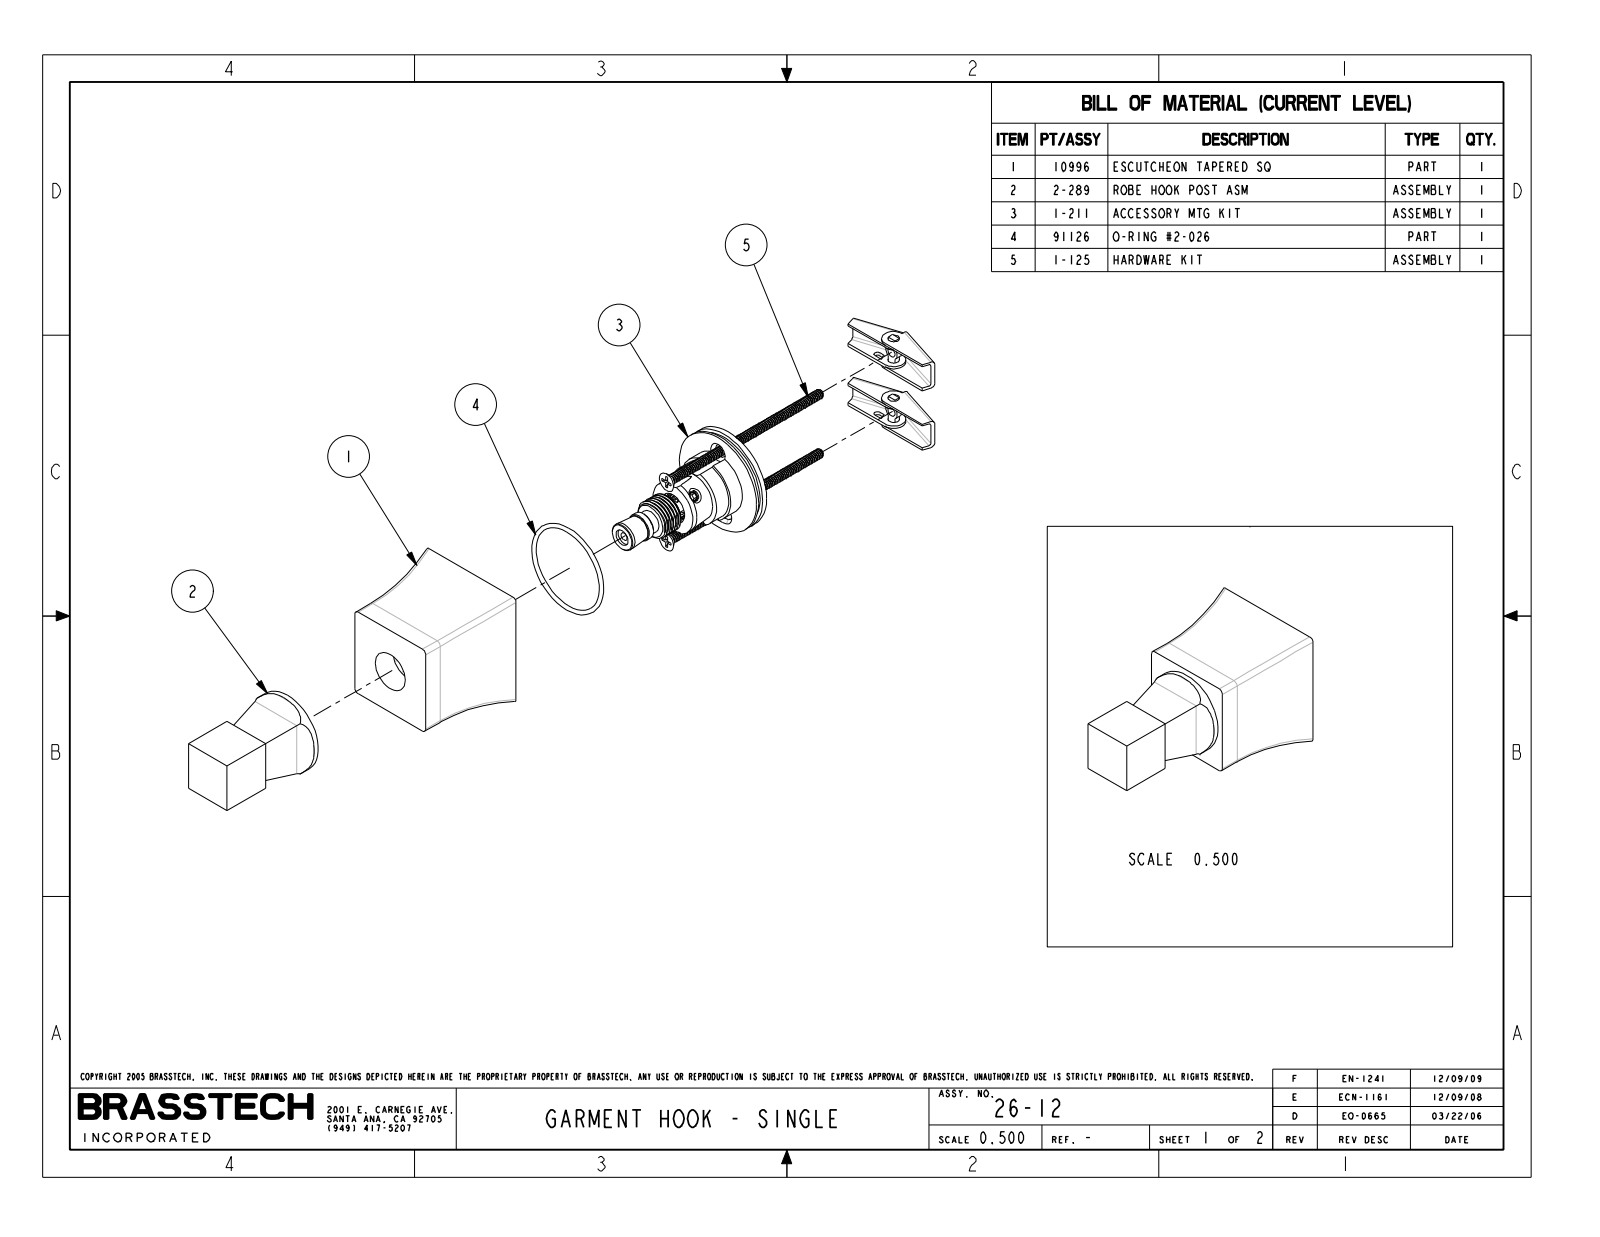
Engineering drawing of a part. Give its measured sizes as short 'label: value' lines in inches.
name: 26-12_WEB
written by: PRO/ENGINEER BY PARAMETRIC TECHNOLOGY CORPORATION, 2009300 (CONFIG_CONTROL_DESIGN)
unit: in
bodies: 0 solids, 65 faces (21 planar, 26 cylindrical, 18 other)
size: 3.12 × 1.75 × 1.75
holes: 1× ⌀0.13
bosses: 1× ⌀1.2
rounds: 4× R0.062, 4× R0.188, 4× R4.5
face distances: 1.57, 0.75, 1.062, 0.313, 2.37, 3.12, 0.8, 1.55, 0.75, 1.375
